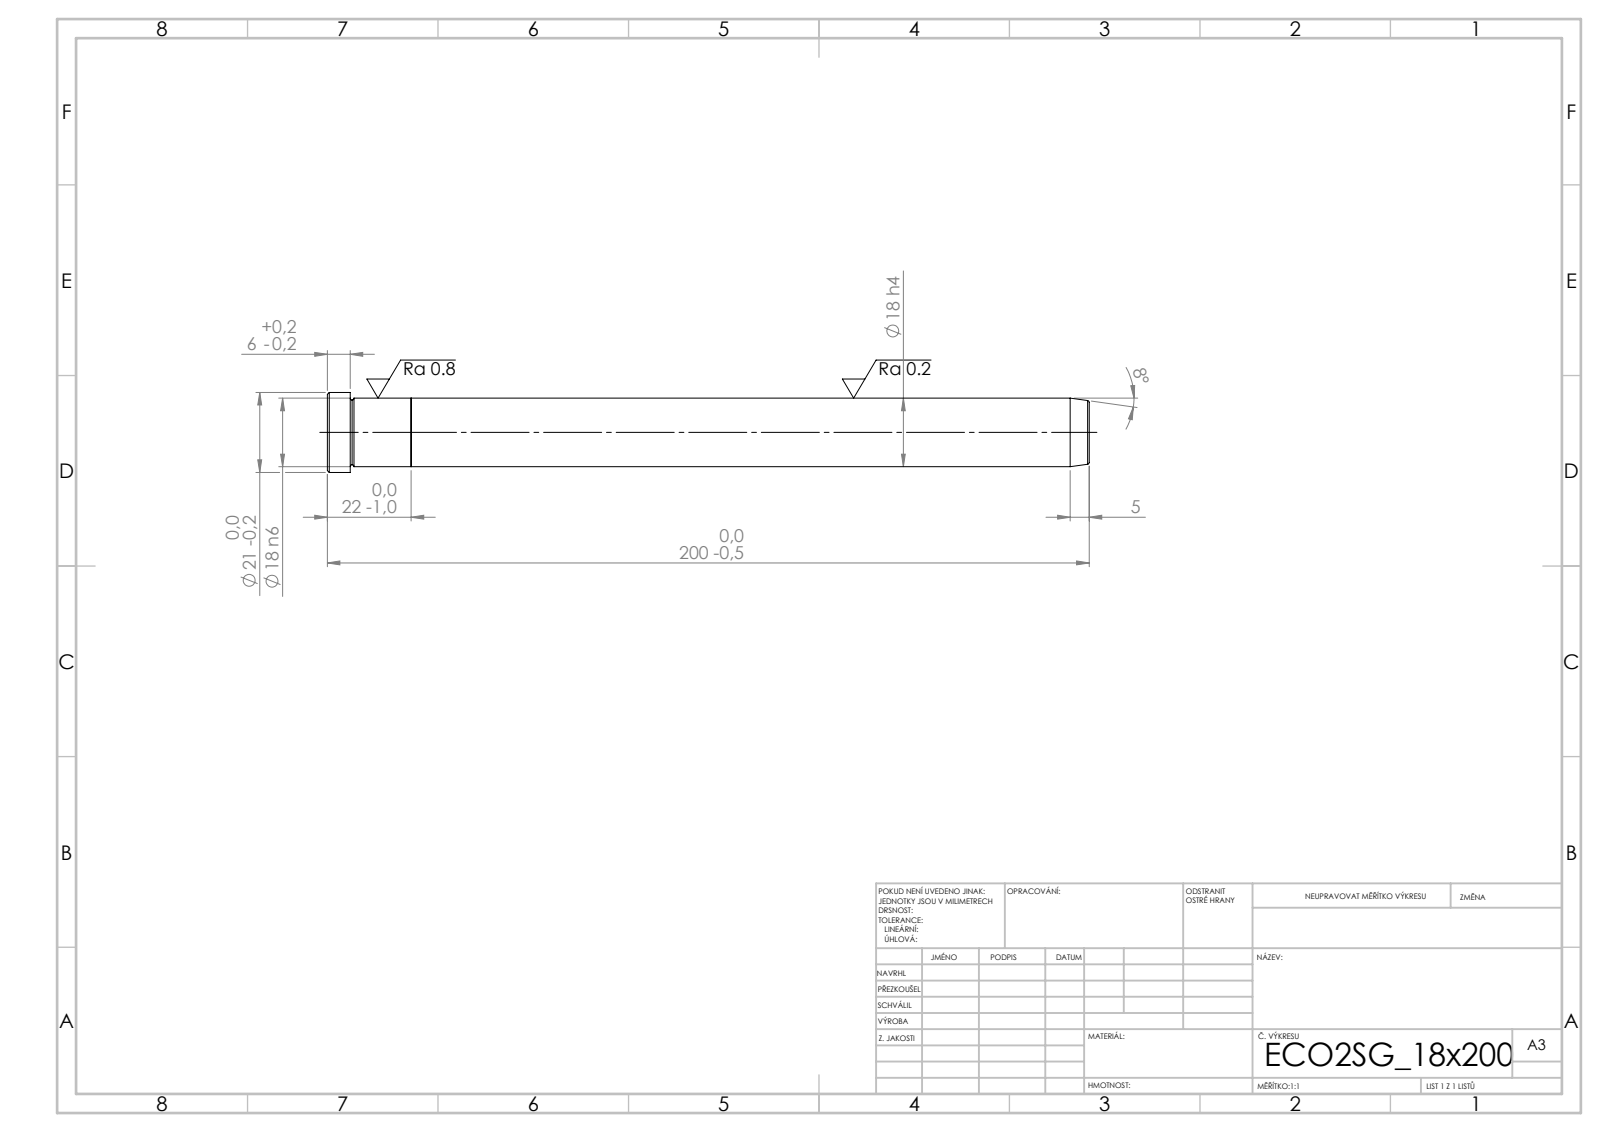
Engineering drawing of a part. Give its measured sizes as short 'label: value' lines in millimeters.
written by: SolidWorks 2019 (CONFIG_CONTROL_DESIGN)
unit: mm
bodies: 2 solids, 21 faces (5 planar, 6 cylindrical, 10 other)
size: 200 × 21 × 21
volume: 51 317 mm³; area: 12 523 mm²
bosses: 1× ⌀21, 1× ⌀18
face distances: 22, 178, 200, 194, 16, 6
